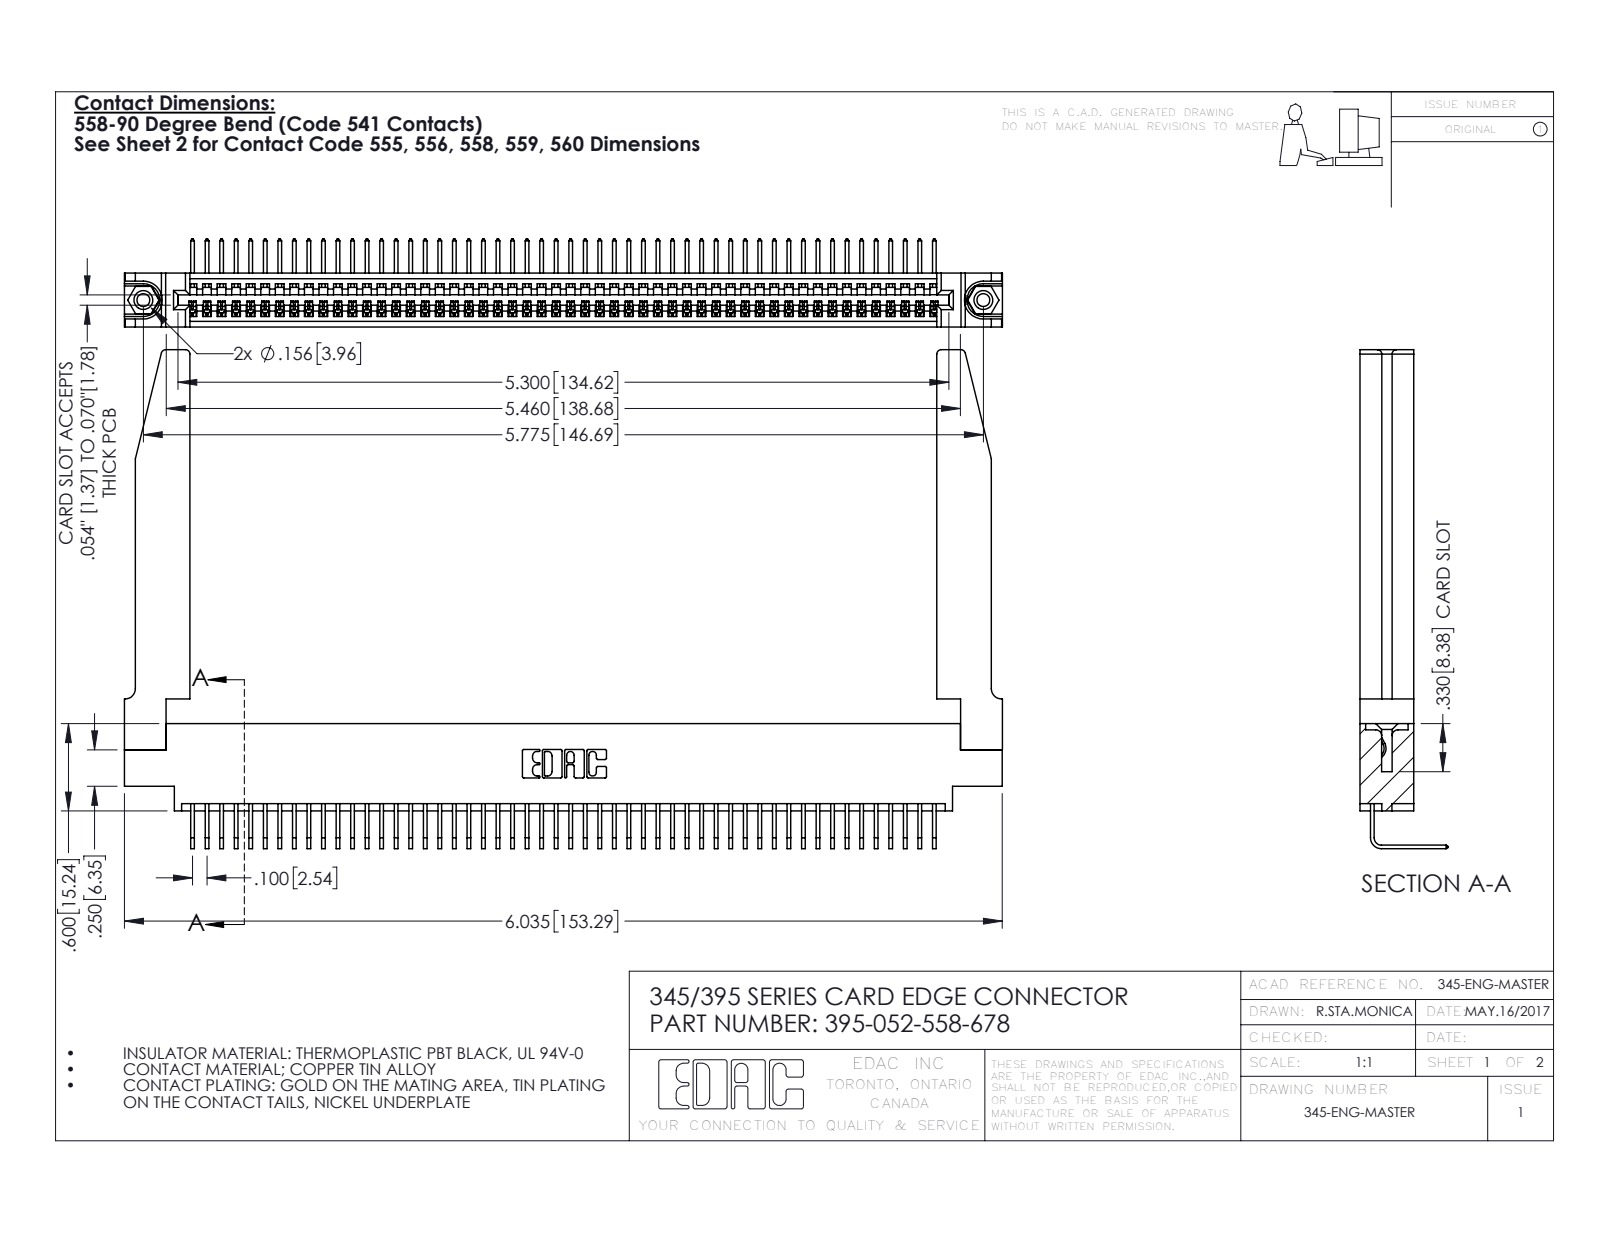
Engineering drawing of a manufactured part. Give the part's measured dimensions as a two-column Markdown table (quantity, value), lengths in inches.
| quantity | value |
| --- | --- |
| part name | 395-052-558-678; 345-220-078_345-220-078; 345 Part_0.170 Offset - 0.156 Dia-TH; 345-250-001_345-250-001-102 (+1 more) |
| STEP written by | SolidWorks 2016 (CONFIG_CONTROL_DESIGN) |
| units | inches |
| bodies | 57 solids, 3484 faces (2410 planar, 1022 cylindrical, 52 other) |
| overall size | 6.036 × 3.429 × 0.605 |
| volume | 1.371 in³ |
| surface area | 42.88 in² |
| round holes (diameter × count) | 0.089 × 2, 0.125 × 2, 0.156 × 2, 0.064 × 1 |
| round bosses / shafts (diameter × count) | 0.155 × 2 |
| partial cylindrical surfaces (radius × count) | 0.006 × 104, 0.01 × 22, 0.03 × 8, 0.007 × 6, 0.031 × 6, 0.026 × 3, 0.031 × 2, 0.04 × 2 |
| main face-to-face distances | 0.37, 0.072, 0.298, 0.098, 0.272, 0.025, 0.2, 0.225, 0.15, 0.148 |
| hole center spacings | 0.27, 5.539, 5.775 |
